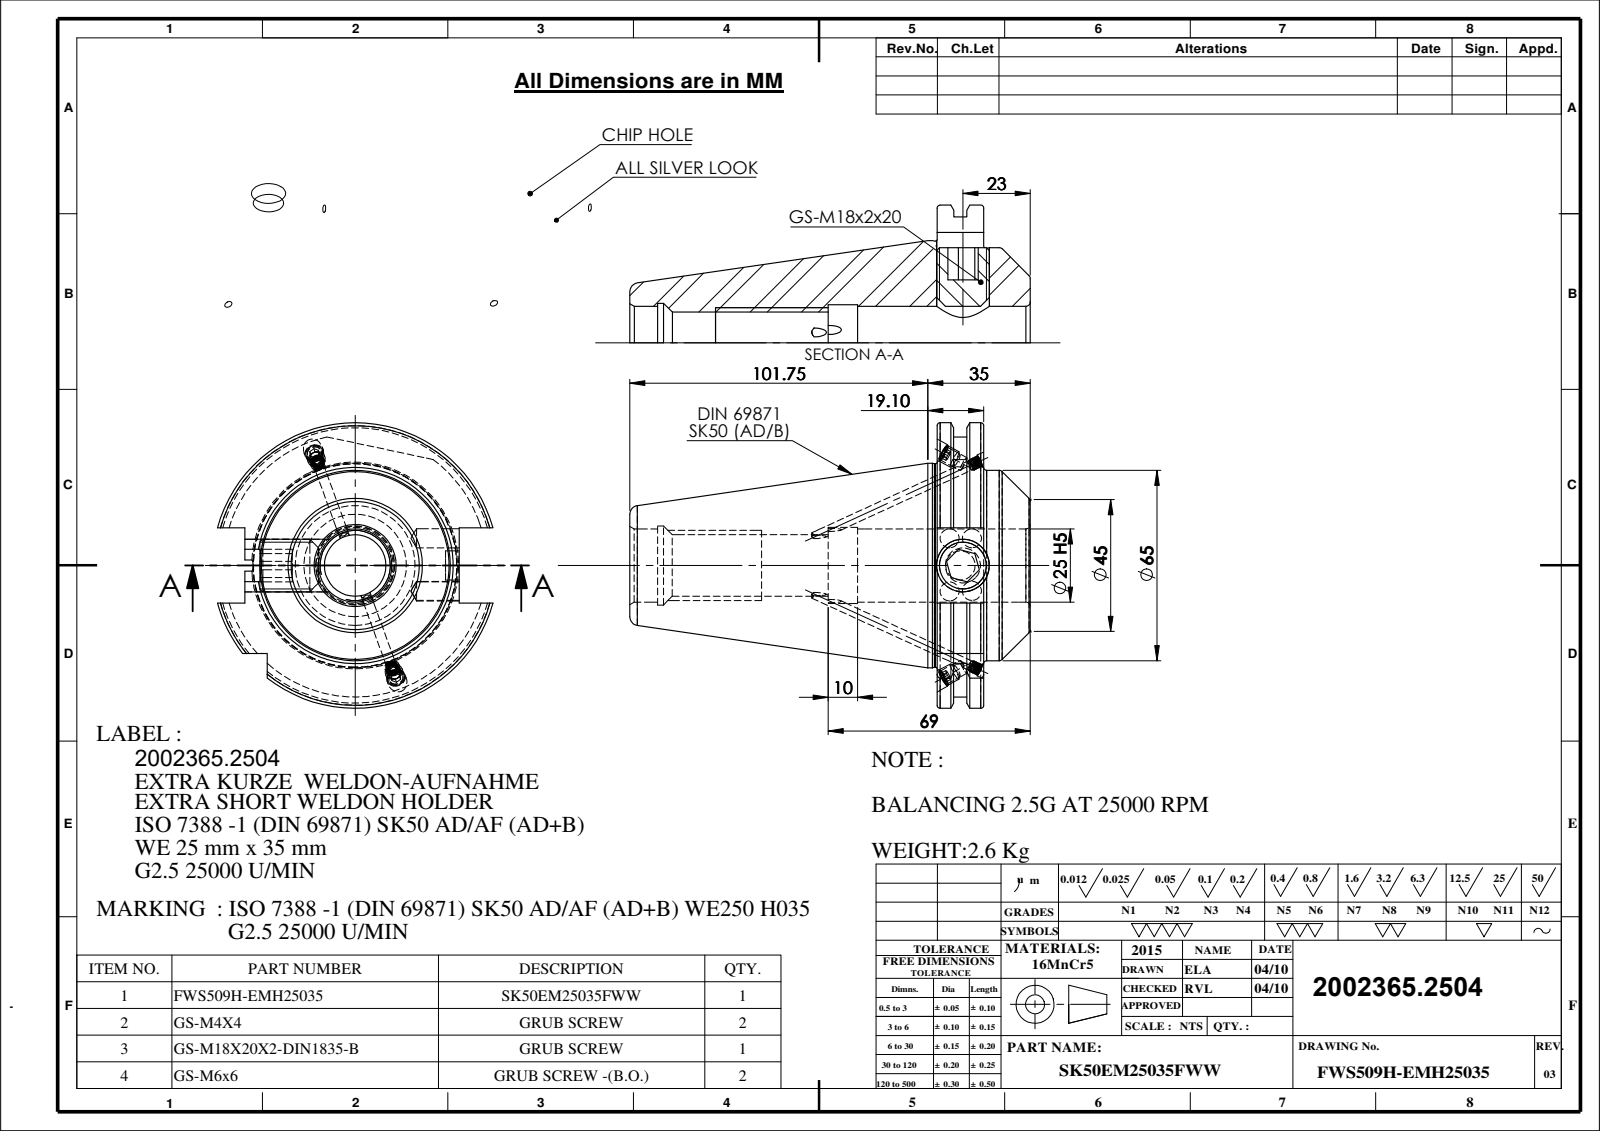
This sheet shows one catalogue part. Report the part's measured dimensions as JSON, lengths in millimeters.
{"part_name": "SK50EM25035FWW-R03; M6X6_DIN 913 - M6 x 6-N; GS-M18X20X2-DIN1835-B; 91506-WE725035 (+2 more)", "step_written_by": "SolidWorks 2018 (CONFIG_CONTROL_DESIGN)", "units": "millimeters", "bodies": {"solids": 6, "faces": 277, "planar": 75, "cylindrical": 83, "other": 119}, "overall_size": [136.75, 97.5, 94.05], "volume_mm3": 340772, "surface_area_mm2": 53623, "round_holes": [[6.5, 6], [3.3, 2], [4.5, 2], [5, 2], [10, 1], [18, 1], [21, 1], [25, 1], [26, 1], [27, 1]], "round_bosses_or_shafts": [[6, 2], [4, 2], [69.85, 1], [69.45, 1], [65, 1]], "partial_cylinders_radius": [[44.9, 1], [48.75, 1]], "face_to_face_distances": [15.9, 31.8, 5.65, 10.25, 26.15, 10.14, 4.49, 5.76, 21.66, 104.95], "hole_center_spacings": [7.61, 0.85, 9.19, 9.51, 9.58, 9.79, 9.94, 9.99]}
